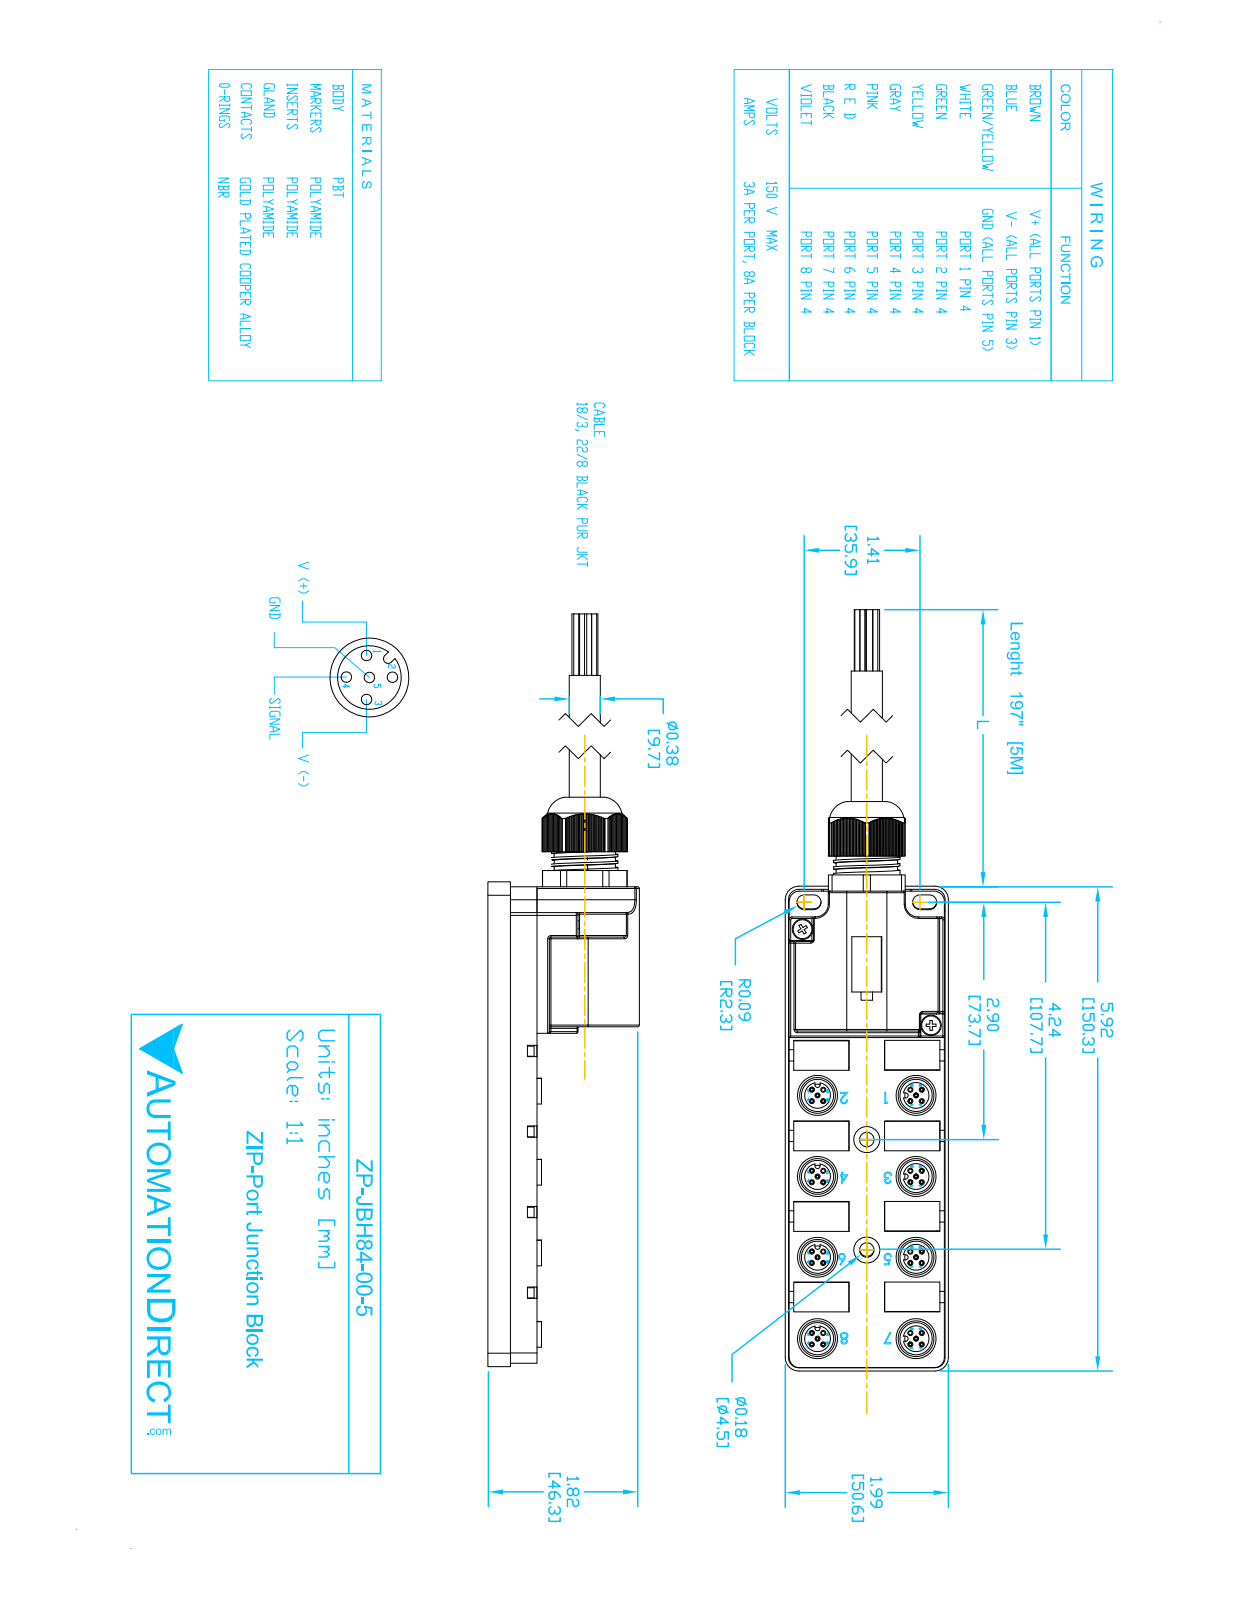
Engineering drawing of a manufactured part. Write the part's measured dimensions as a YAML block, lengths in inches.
part_name: "ZP-JBH84-2P-5"
step_written_by: "SolidWorks 2017 (AUTOMOTIVE_DESIGN)"
units: inches
bodies: {solids: 10, faces: 1533, planar: 863, cylindrical: 395, other: 275}
overall_size: [9.168, 1.991, 1.851]
volume: 10.57
surface_area: 62.84
round_holes:
  - {diameter: 0.043, count: 40}
  - {diameter: 0.063, count: 40}
  - {diameter: 0.437, count: 8}
  - {diameter: 0.488, count: 8}
  - {diameter: 0.177, count: 2}
  - {diameter: 0.25, count: 2}
  - {diameter: 0.26, count: 2}
  - {diameter: 0.318, count: 2}
  - {diameter: 0.3, count: 1}
  - {diameter: 0.37, count: 1}
  - {diameter: 0.49, count: 1}
  - {diameter: 0.597, count: 1}
round_bosses_or_shafts:
  - {diameter: 0.315, count: 7}
  - {diameter: 0.23, count: 2}
  - {diameter: 0.81, count: 1}
  - {diameter: 0.345, count: 1}
  - {diameter: 0.315, count: 1}
partial_cylinders:
  - {radius: 0.02, count: 34}
  - {radius: 0.031, count: 8}
  - {radius: 0.035, count: 4}
  - {radius: 0.09, count: 4}
  - {radius: 0.164, count: 4}
  - {radius: 0.126, count: 2}
  - {radius: 0.156, count: 2}
  - {radius: 0.625, count: 2}
face_to_face_distances: [0.6, 0.035, 0.035, 0.031, 0.6, 0.565, 1.896, 0.596, 1.944, 0.048]
hole_center_spacings: [0.098, 0.139, 1.204, 1.136, 1.275, 0.991, 1.559, 0.197]
